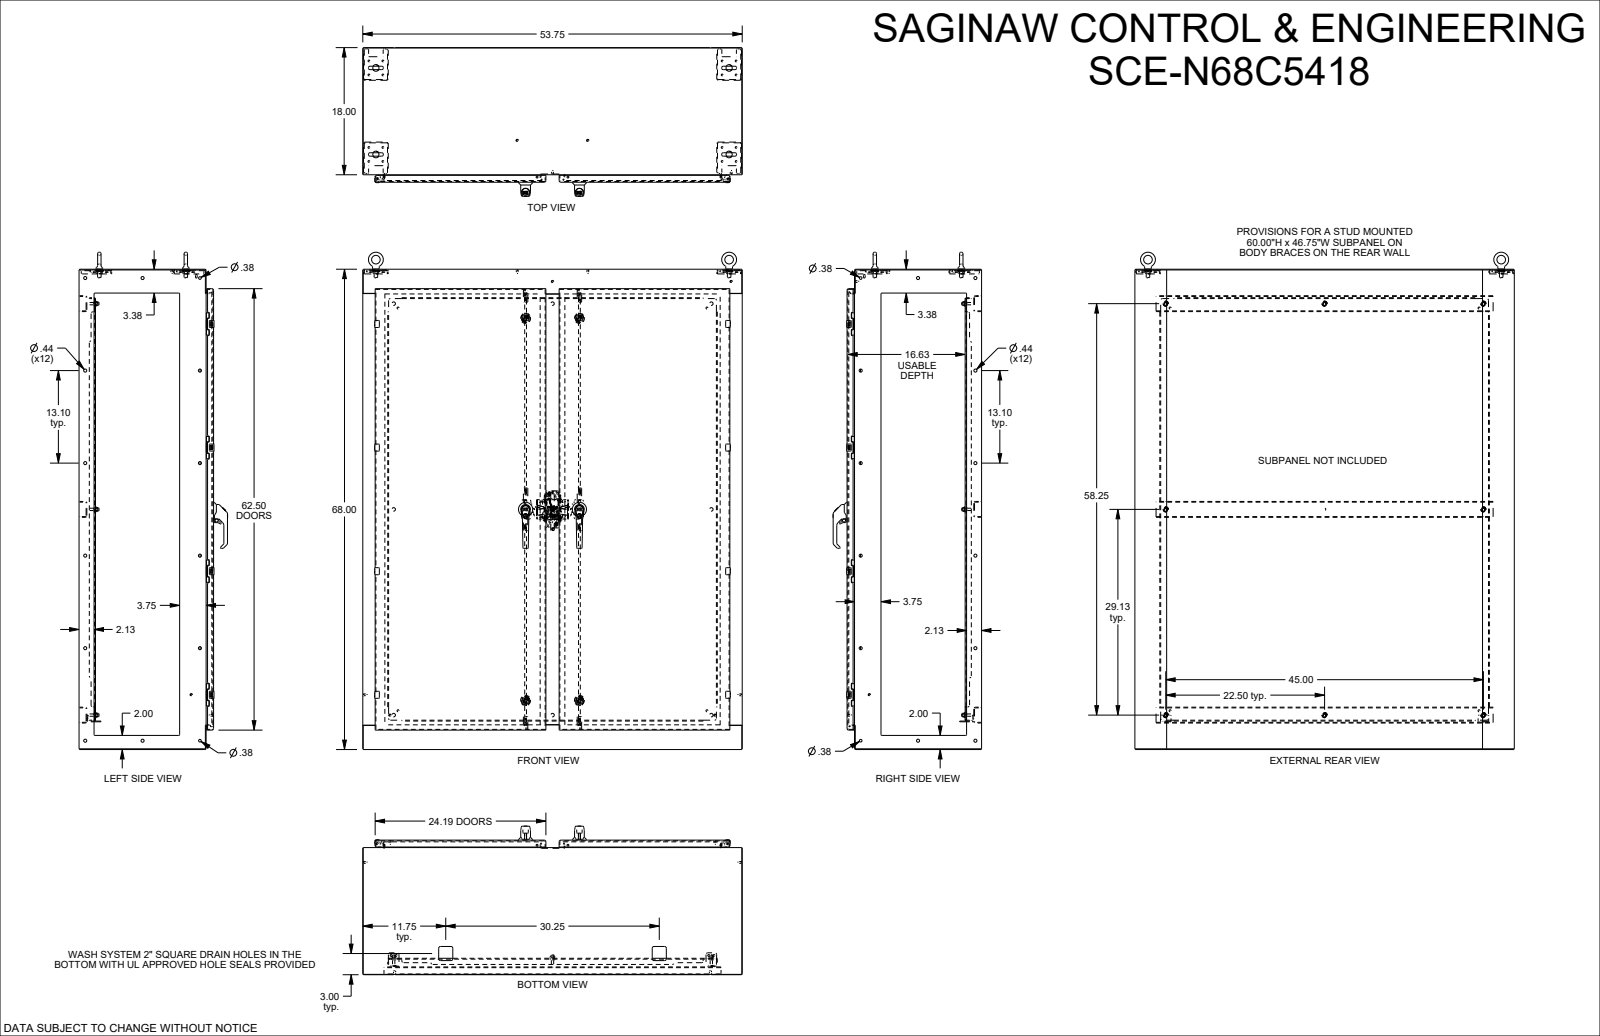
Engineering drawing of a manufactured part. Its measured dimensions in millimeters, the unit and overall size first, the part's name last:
Units: millimetres
Overall size (bounding box): 1788.7 × 1365.3 × 534.6
Round holes (diameter × count): ⌀6.4 ×20, ⌀9.5 ×18, ⌀6.2 ×16, ⌀5.5 ×12, ⌀11.1 ×12, ⌀1 ×8, ⌀4.3 ×8, ⌀5.2 ×8, ⌀5.2 ×8, ⌀3.4 ×4, ⌀6.5 ×4, ⌀6.8 ×4
Round bosses / shafts (diameter × count): ⌀4.3 ×24, ⌀6.4 ×20, ⌀6.1 ×16, ⌀5 ×10, ⌀35.6 ×4, ⌀25.4 ×4, ⌀18.5 ×4, ⌀8.7 ×4
Partial cylindrical surfaces — rounded edges, fillets, slot ends (radius × count): R0.8 ×250, R0.4 ×162, R0.5 ×150, R3.2 ×98, R0.5 ×48, R1 ×42, R1 ×40, R4.2 ×38
Main face-to-face distances: 2.6, 481.4, 478.8, 484.1, 454.6, 26.9, 1724.6, 451.9, 29.5, 457.2
Hole centre spacings: 444.5, 50.3, 889, 35.6, 311.2, 332.7, 530.2, 1241.3
Volume: 22 090 000 mm³ · Surface area: 15 960 000 mm²
Bodies: 67 solids, 8175 faces (3224 planar, 2711 cylindrical, 2240 other)
Part name (STEP PRODUCT): SCE-N68C5418
STEP written by: SolidWorks 2023 (AUTOMOTIVE_DESIGN)
